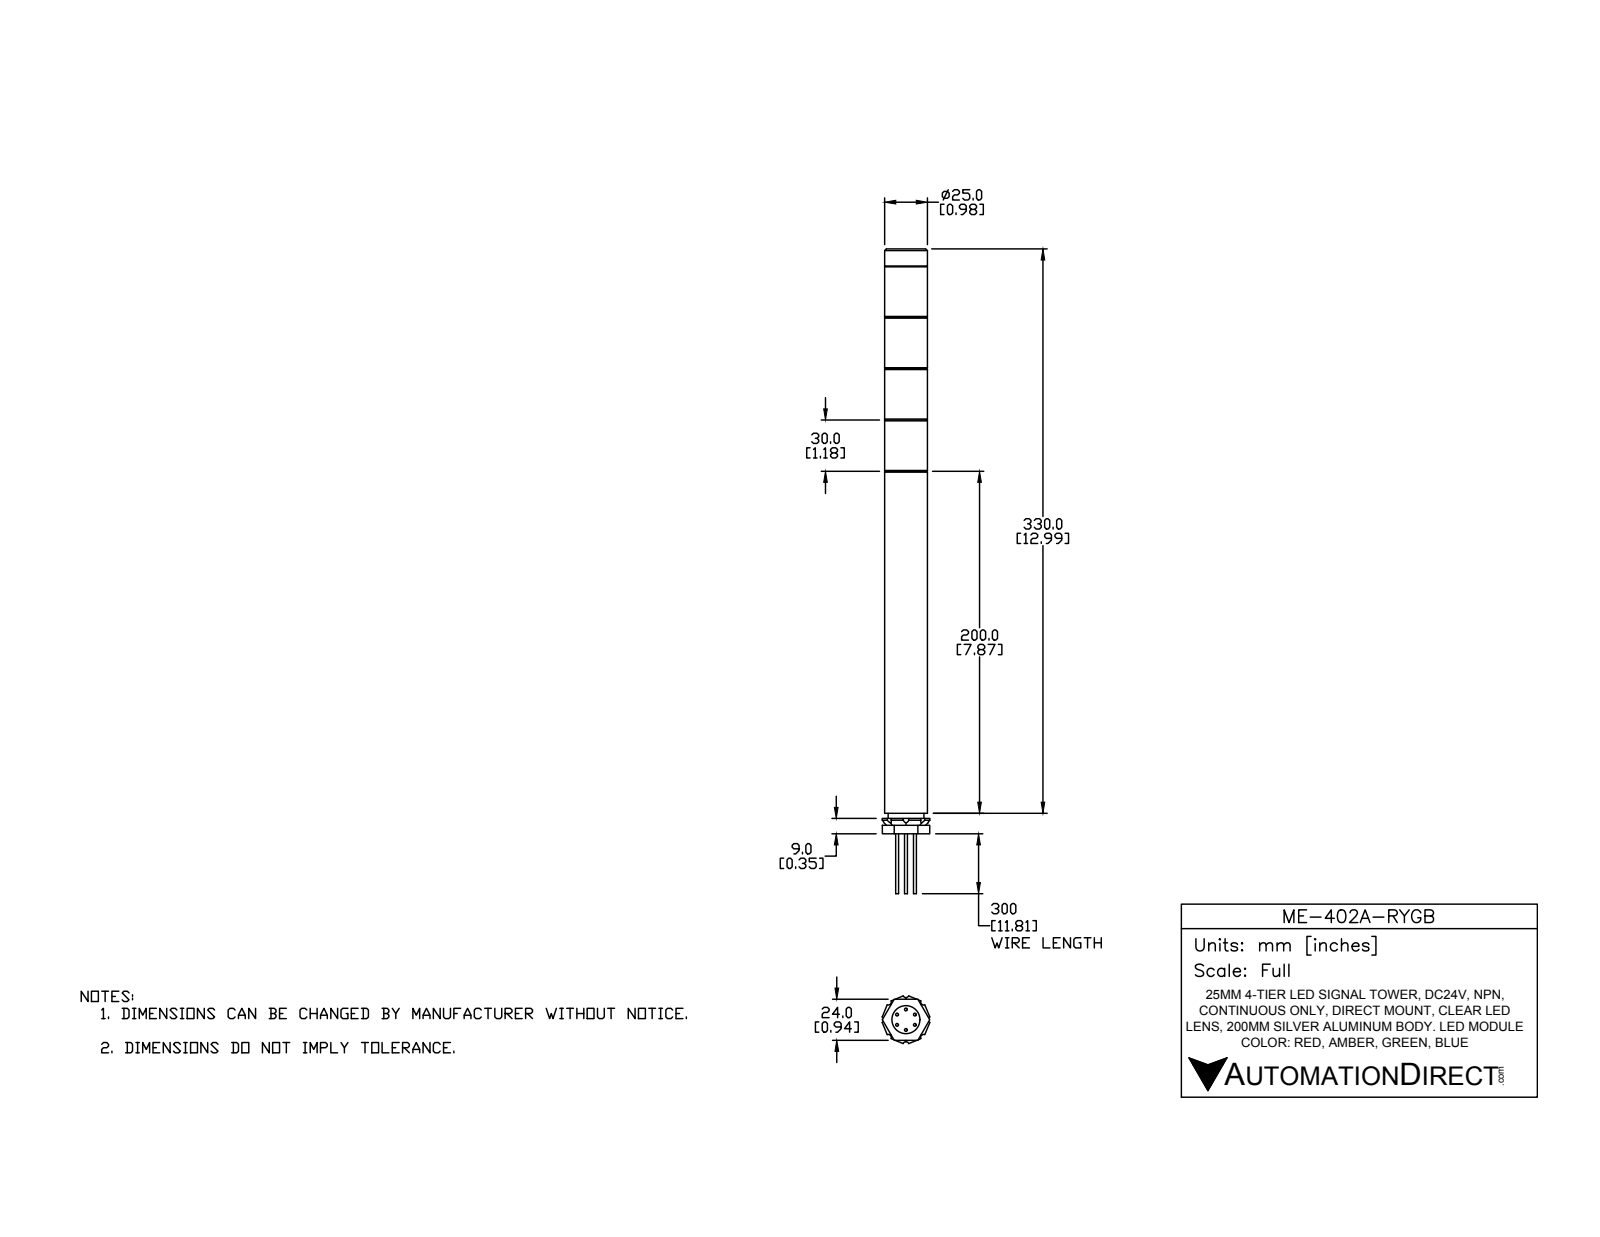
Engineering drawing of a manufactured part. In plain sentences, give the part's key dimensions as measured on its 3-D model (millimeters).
The part is named "ME-402A-RYGB". Its 3-D file was written by "SolidWorks 2016 (AUTOMOTIVE_DESIGN)". It is 15 solids with 156 faces: 77 planar, 53 cylindrical and 26 other. Overall it measures 377 by 27.89 by 27.89 millimeters. Its volume is 156 335 cubic millimeters and its surface area 41 143 square millimeters. Round holes: 1 of diameter 3.2, 1 of diameter 7.7, 1 of diameter 16.4, 1 of diameter 18, 1 of diameter 20.7, 1 of diameter 21. Round bosses or shafts: 6 of diameter 1.7, 1 of diameter 25, 1 of diameter 20.9, 1 of diameter 16, 1 of diameter 5. Partial cylindrical surfaces (rounded edges, fillets, slot ends): 8 of radius 1.75. The main face-to-face distances are 30, 60, 90, 120, 40, 297, 167, 197, 227, 257.
